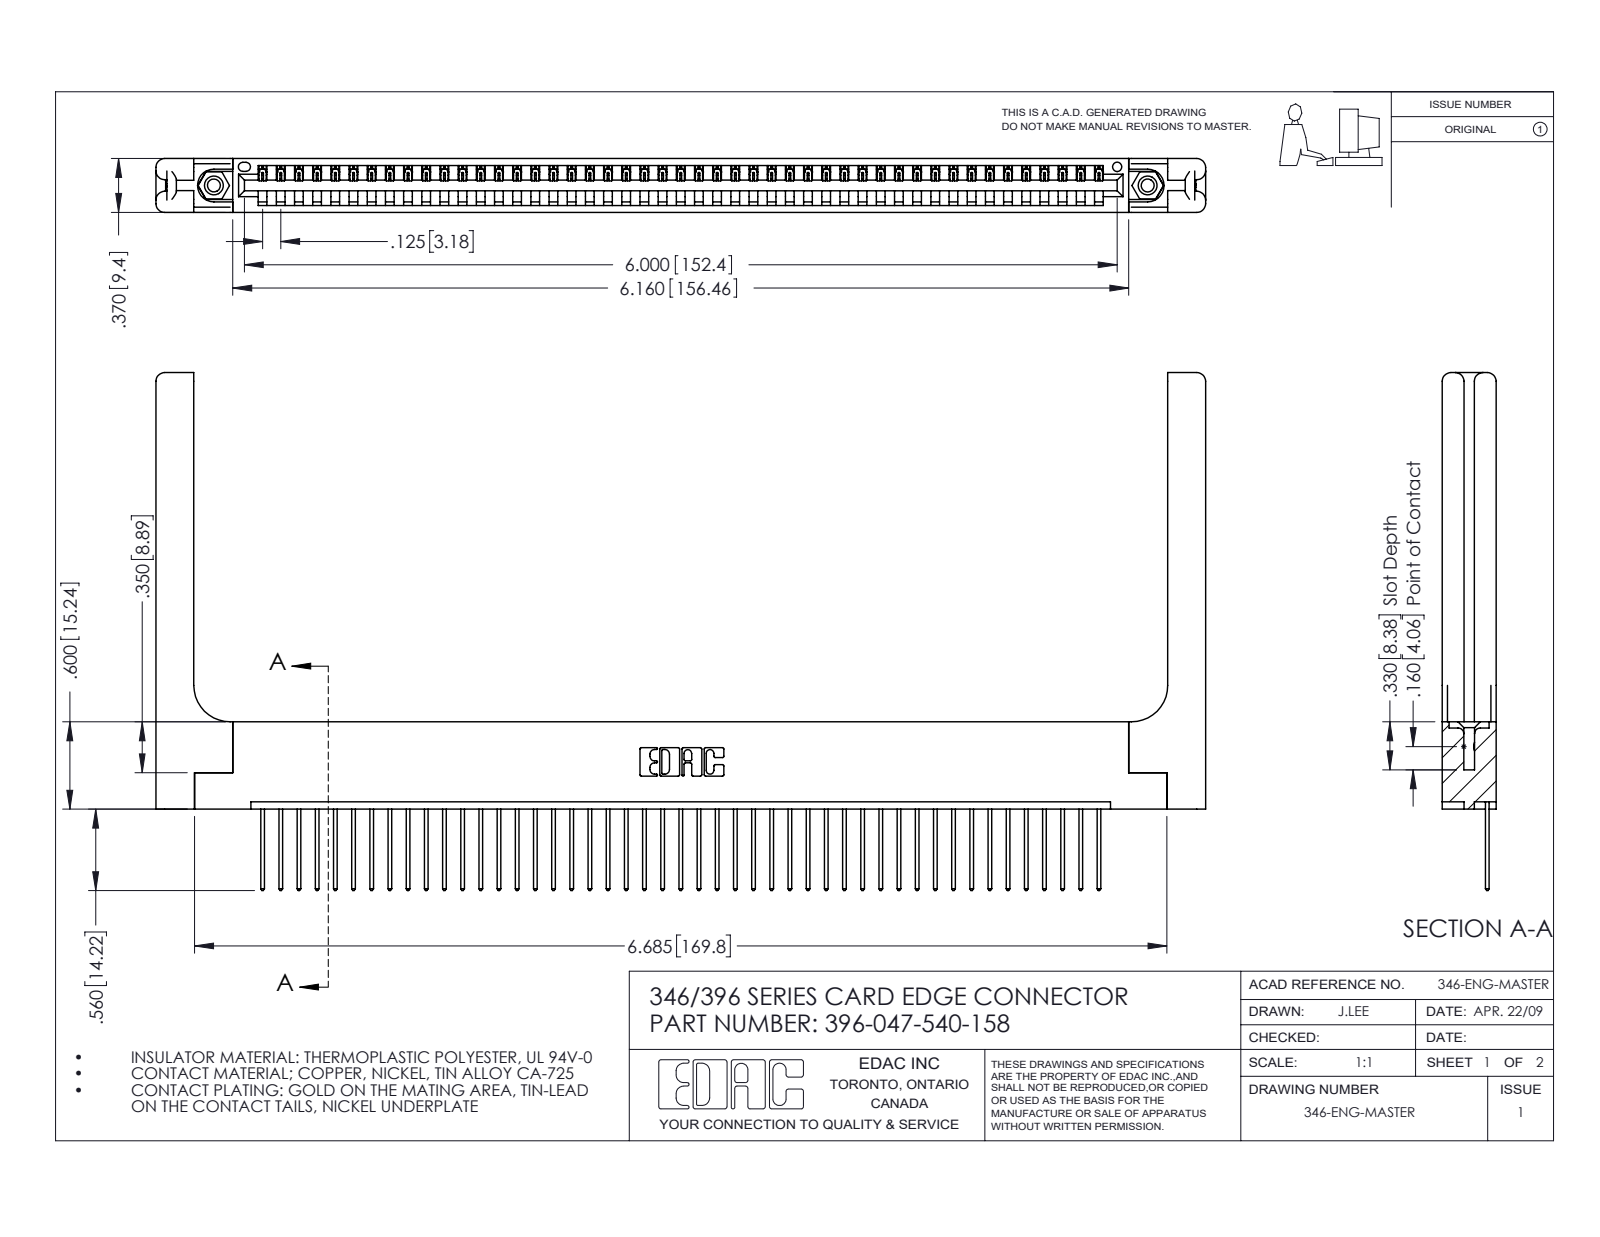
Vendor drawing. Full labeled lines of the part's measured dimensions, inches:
Part name (STEP PRODUCT): 346-220-058_345-220-058; 345-250-001_345-250-001-102; 345-292-001_345-293-140; 396-047-540-158 (+1 more)
STEP written by: SolidWorks 2016 (CONFIG_CONTROL_DESIGN)
Units: inches
Bodies: 52 solids, 3104 faces (2104 planar, 940 cylindrical, 60 other)
Overall size (bounding box): 7.216 × 3.56 × 0.37
Volume: 1.535 in³ · Surface area: 43 in²
Round holes (diameter × count): ⌀0.089 ×2, ⌀0.125 ×2, ⌀0.156 ×2, ⌀0.064 ×1
Round bosses / shafts (diameter × count): ⌀0.155 ×2
Partial cylindrical surfaces — rounded edges, fillets, slot ends (radius × count): R0.006 ×94, R0.01 ×94, R0.01 ×22, R0.06 ×16, R0.007 ×6, R0.031 ×6, R0.026 ×3, R0.03 ×2
Main face-to-face distances: 0.37, 0.048, 0.322, 0.072, 0.148, 0.15, 0.25, 0.298, 0.025, 0.222
Hole centre spacings: 0.246, 6.211, 6.42
